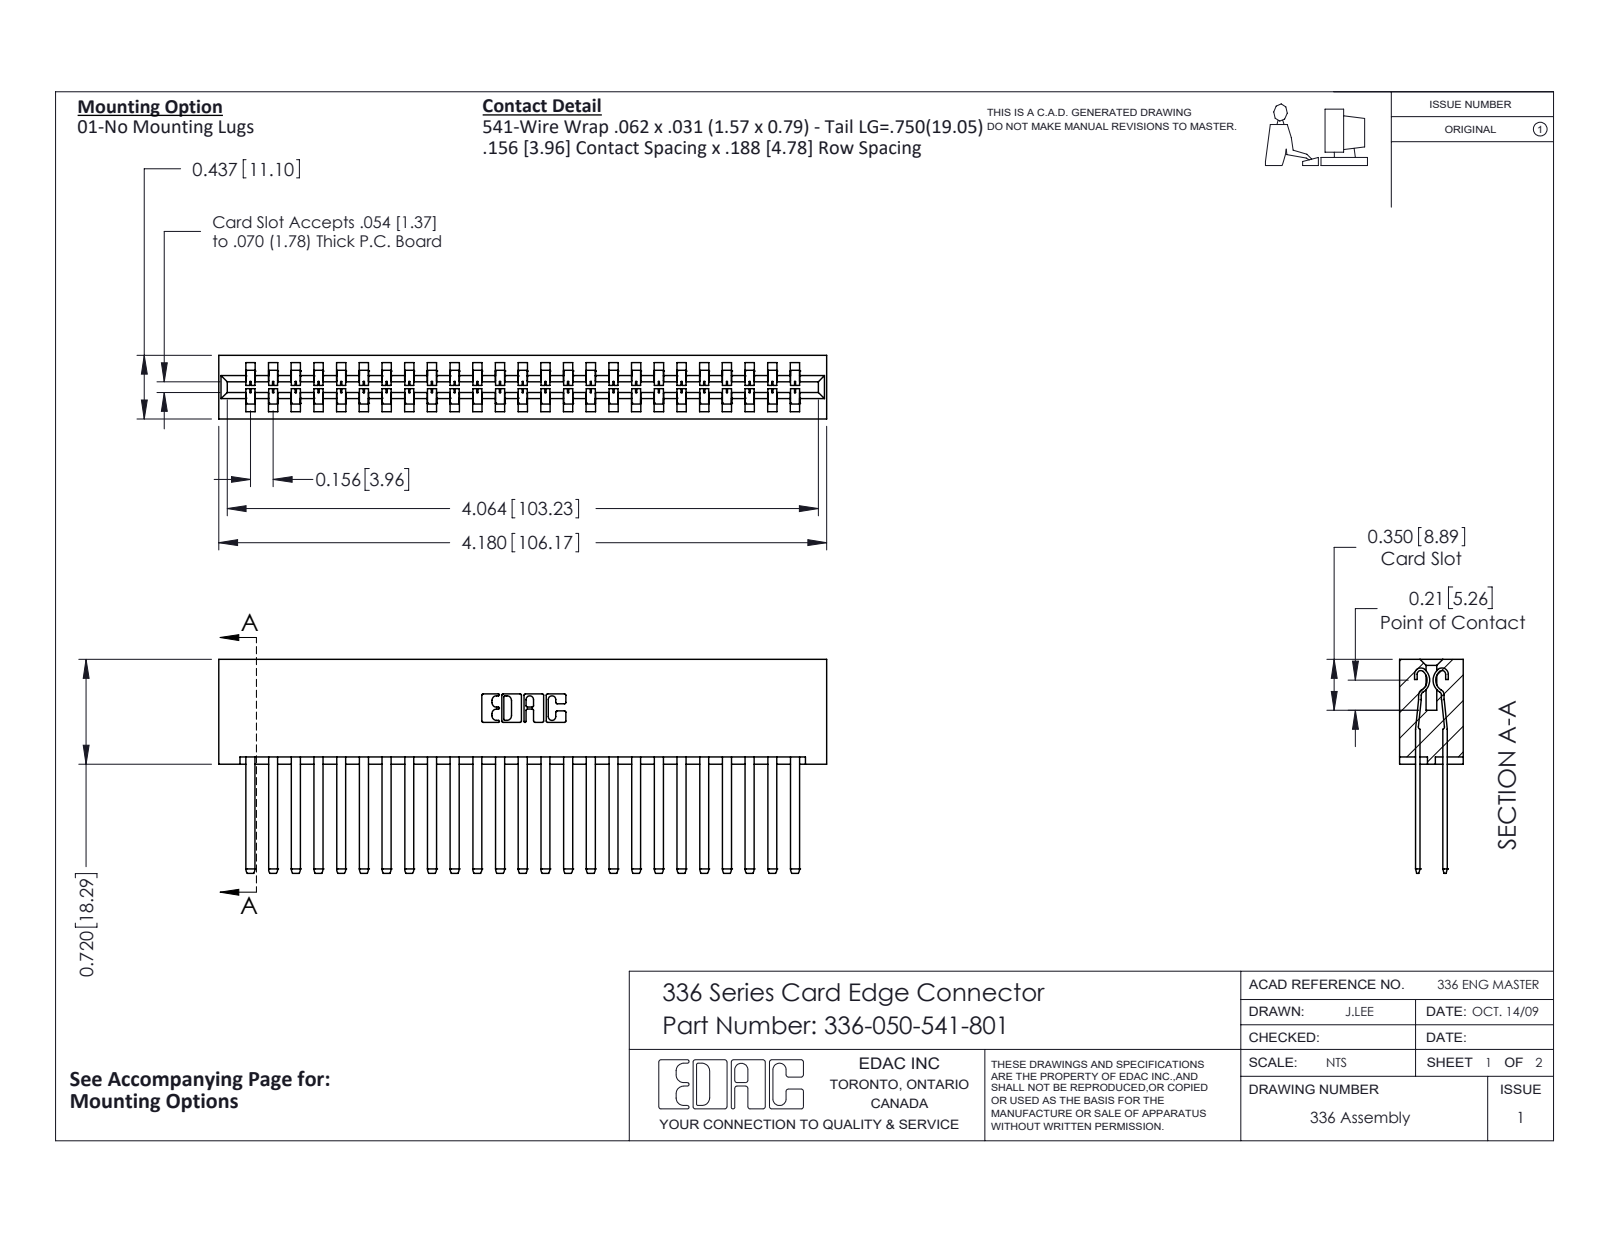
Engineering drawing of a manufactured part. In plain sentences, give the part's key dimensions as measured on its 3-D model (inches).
The part is named "336-050-541-801; 336 Part_Lugless; 336-290-001_336-290-541". Its 3-D file was written by "SolidWorks 2020 (CONFIG_CONTROL_DESIGN)". It is 51 solids with 2206 faces: 1366 planar, 840 cylindrical and 0 other. Overall it measures 4.18 by 1.47 by 0.437 inches. Its volume is 1.07 cubic inches and its surface area 34.52 square inches. Partial cylindrical surfaces (rounded edges, fillets, slot ends): 100 of radius 0.004, 50 of radius 0.056, 22 of radius 0.01, 6 of radius 0.007, 6 of radius 0.031, 4 of radius 0.022, 4 of radius 0.04, 3 of radius 0.026. The main face-to-face distances are 0.188, 0.328, 0.14, 0.297, 0.109, 0.031, 0.437, 0.033, 0.181, 0.256.
